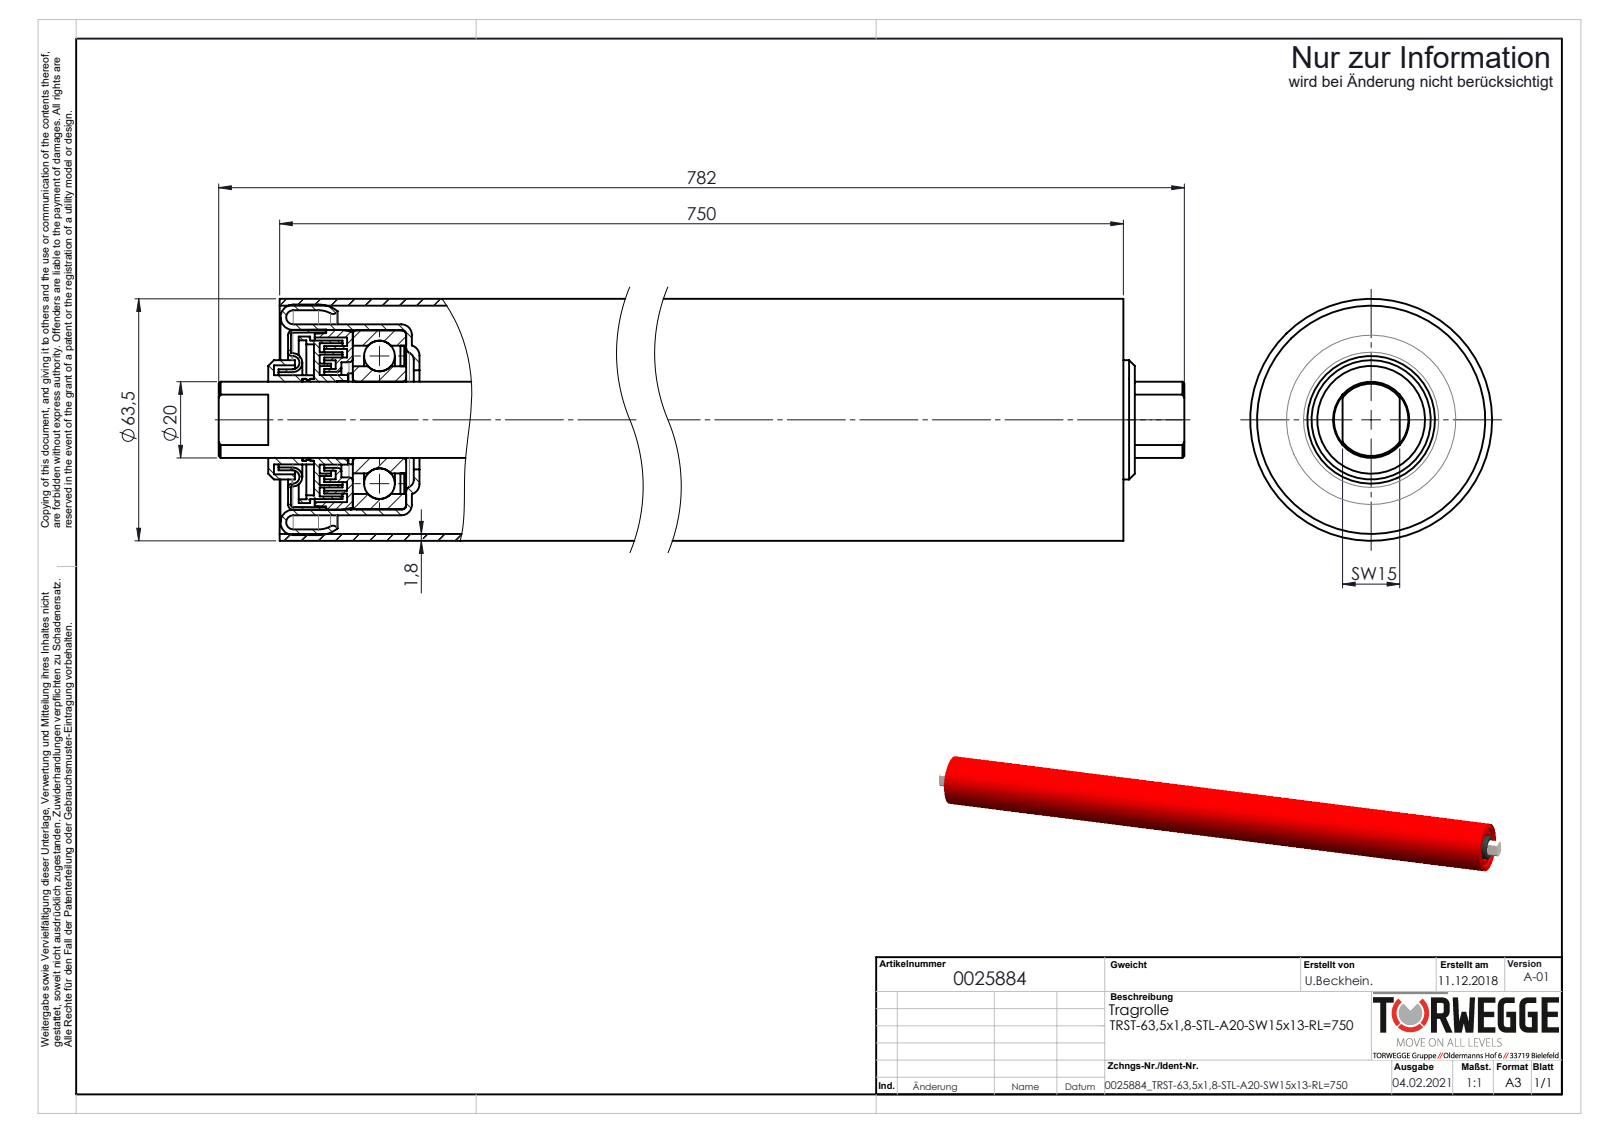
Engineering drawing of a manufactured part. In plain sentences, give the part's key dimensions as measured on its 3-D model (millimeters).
The part is named "0025884". Its 3-D file was written by "SolidWorks 2020 (AUTOMOTIVE_DESIGN)". It is 22 solids with 498 faces: 102 planar, 220 cylindrical and 176 other. Overall it measures 782 by 63.5 by 63.5 millimeters. Its volume is 597 459 cubic millimeters and its surface area 457 206 square millimeters. Round holes: 4 of diameter 2, 1 of diameter 19, 1 of diameter 19.6, 1 of diameter 20, 1 of diameter 20.3, 1 of diameter 21.5, 1 of diameter 25, 1 of diameter 25.2, 1 of diameter 26, 1 of diameter 28.2, 1 of diameter 28.6, 1 of diameter 30.2. Round bosses or shafts: 2 of diameter 23.9, 1 of diameter 63.5, 1 of diameter 60.5, 1 of diameter 50.1, 1 of diameter 47.2, 1 of diameter 47, 1 of diameter 43.7, 1 of diameter 41.6. Partial cylindrical surfaces (rounded edges, fillets, slot ends): 8 of radius 2, 1 of radius 13.5. The main face-to-face distances are 1.5, 14, 707.8, 721.8, 22.7, 8.7, 699.1, 720.3, 15.5, 697.6. The hole center spacings are 11.49, 4, 11.5, 21.63, 22.65, 22.66, 22.99.
